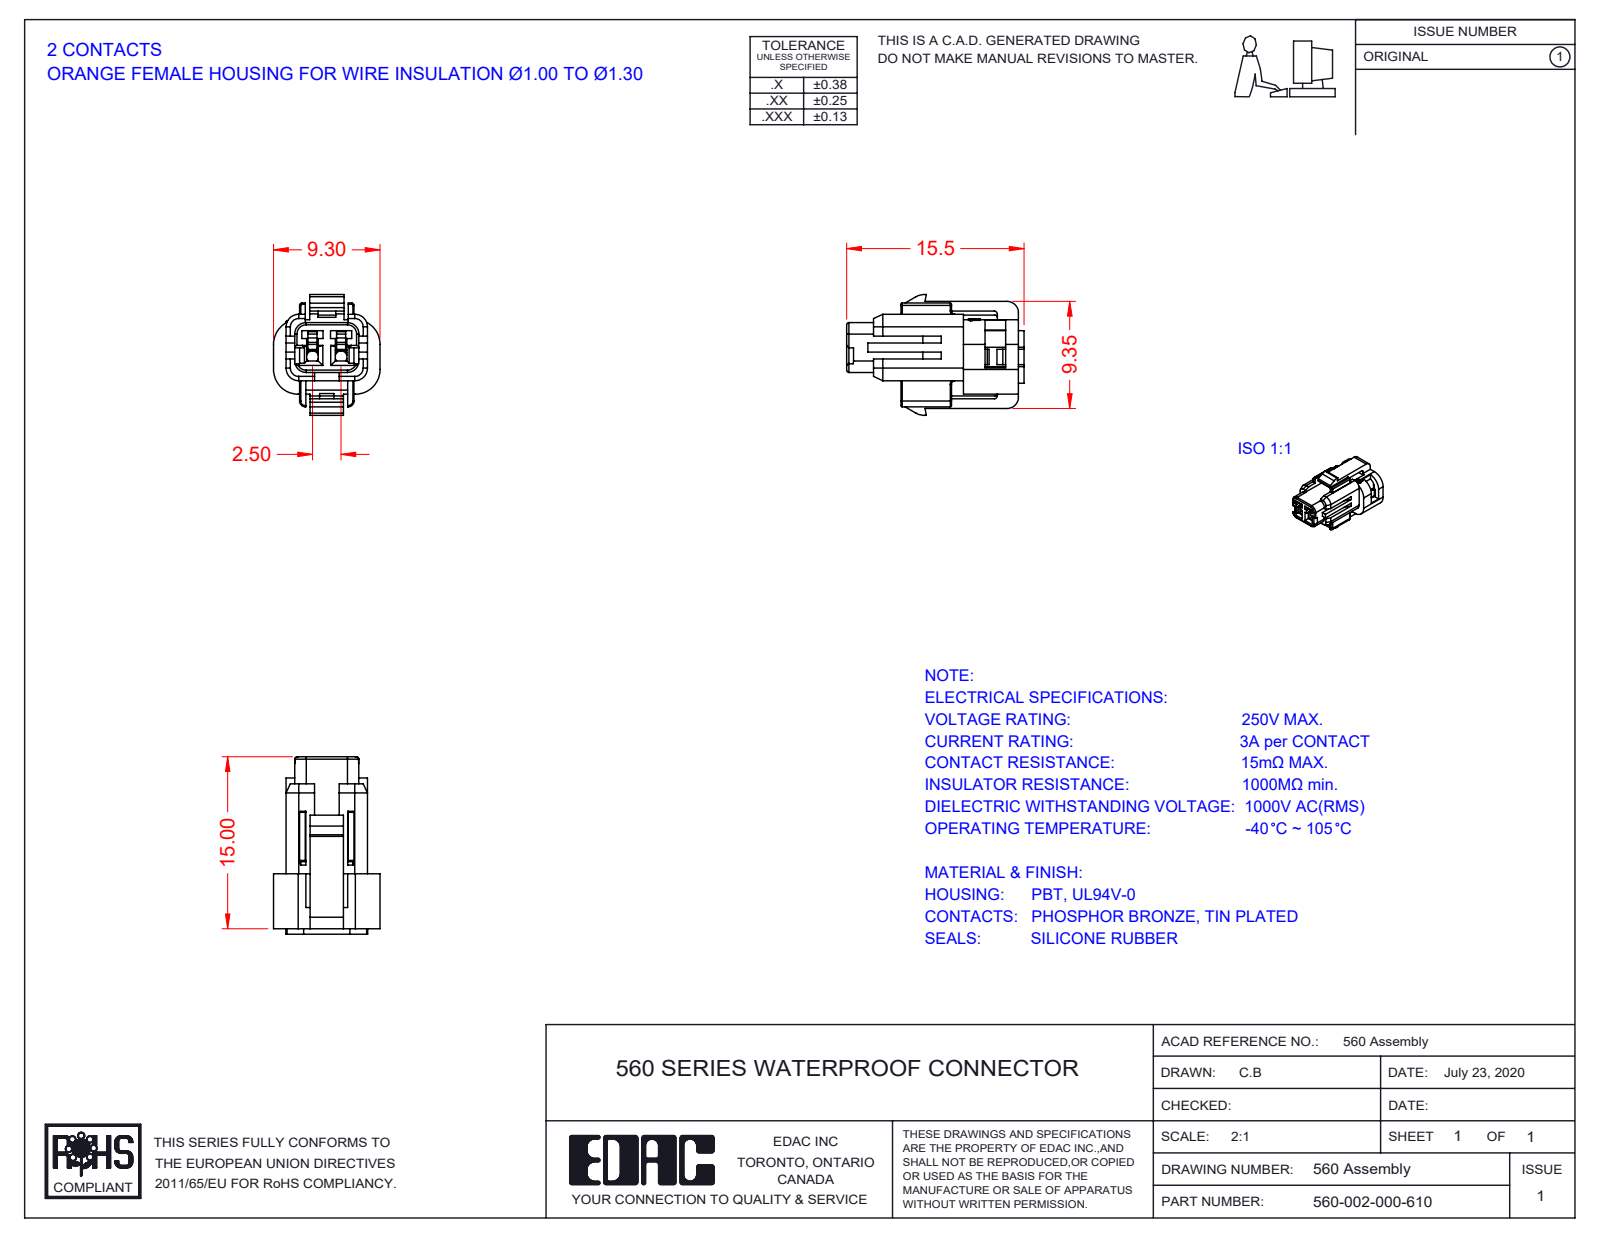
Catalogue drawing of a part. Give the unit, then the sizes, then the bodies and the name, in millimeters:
Units: millimetres
Overall size (bounding box): 15.48 × 10.55 × 9.3
Round holes (diameter × count): ⌀1.5 ×2
Partial cylindrical surfaces — rounded edges, fillets, slot ends (radius × count): R0.1 ×14, R1.2 ×12, R0.2 ×10, R1 ×10, R0.15 ×8, R0.3 ×4, R0.8 ×4, R1.1 ×4
Main face-to-face distances: 0.7, 3.8, 4, 0.8, 1.85, 3.1, 2.5, 1.6, 1.5, 0.9
Hole centre spacings: 2.5
Volume: 545 mm³ · Surface area: 1 381 mm²
Bodies: 3 solids, 656 faces (401 planar, 139 cylindrical, 116 other)
Part name (STEP PRODUCT): 560-002-000-610; FEMALE-HOUSING-2POS_ORANGE; INSULATOR-2POS-1; REAR-GASKET-2POS_YELLOW
STEP written by: SolidWorks 2020 (CONFIG_CONTROL_DESIGN)
